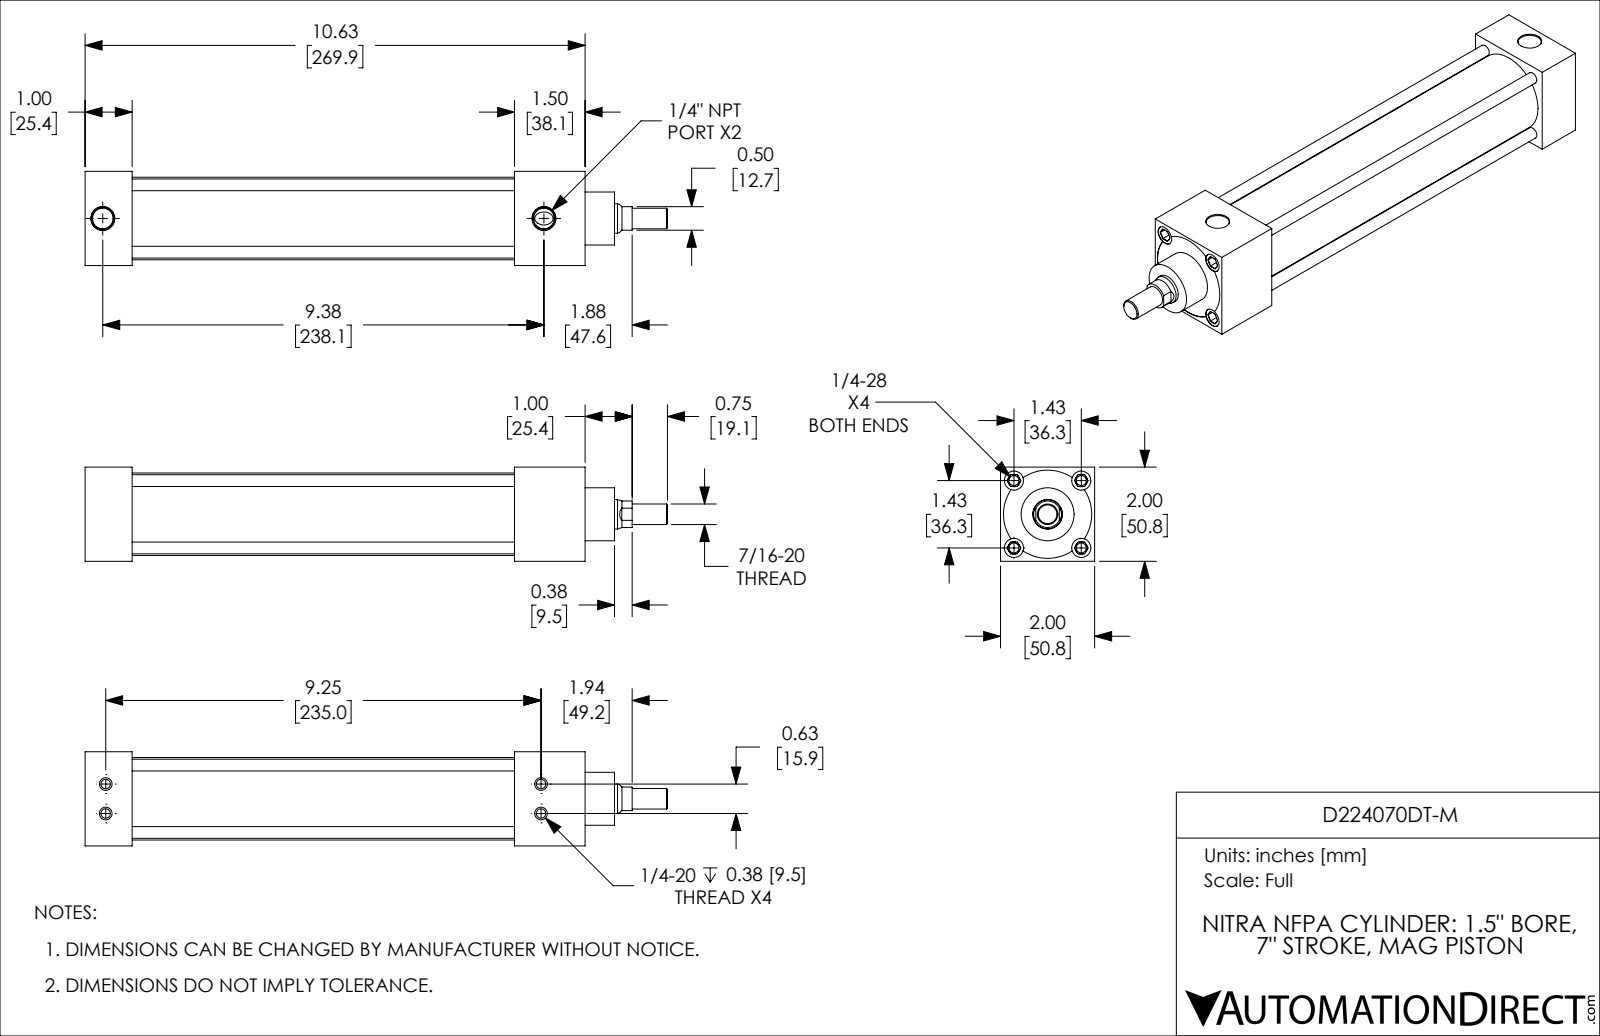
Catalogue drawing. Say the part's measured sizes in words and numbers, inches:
The part is named "D224070DT-M_BODY; D224070DT-M_PISTON_KK1; D224070DT-M". Its 3-D file was written by "SolidWorks 2019 (CONFIG_CONTROL_DESIGN)". It is 2 solids with 203 faces: 58 planar, 65 cylindrical and 80 other. Overall it measures 12.375 by 2 by 2 inches. Its volume is 21.16 cubic inches and its surface area 184.5 square inches. Round holes: 4 of diameter 0.201, 4 of diameter 0.213, 4 of diameter 0.406, 2 of diameter 0.438, 1 of diameter 0.626, 1 of diameter 1.501. Round bosses or shafts: 4 of diameter 0.25, 1 of diameter 1.751, 1 of diameter 1.499, 1 of diameter 1.125, 1 of diameter 0.624, 1 of diameter 0.437. Partial cylindrical surfaces (rounded edges, fillets, slot ends): 1 of radius 0.281, 1 of radius 0.937. The main face-to-face distances are 2, 1, 9.125, 8.125, 10.62, 9.62, 1.495, 1.125, 2.125, 7. The hole center spacings are 0.319, 1.011, 1.43, 0.625, 2.022, 9.25, 9.271, 9.317.
